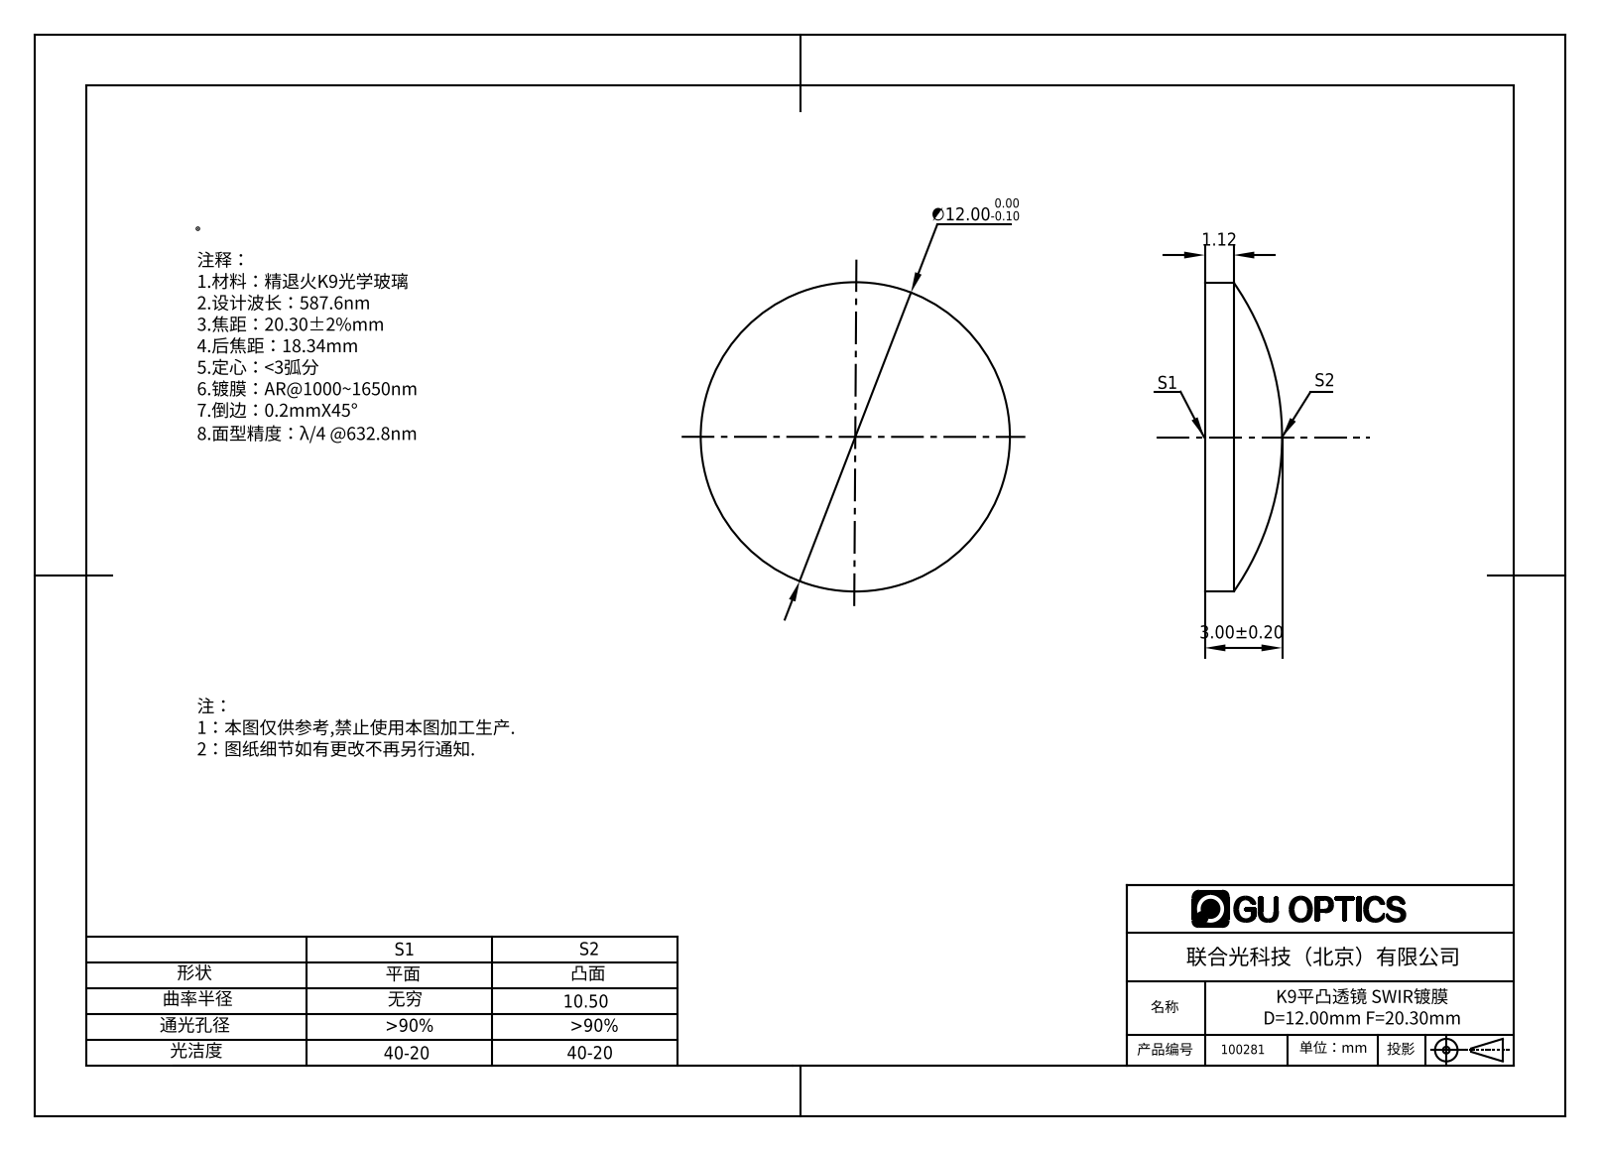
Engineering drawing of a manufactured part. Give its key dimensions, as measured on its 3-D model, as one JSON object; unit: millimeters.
{"part_name": "100109", "step_written_by": "SolidWorks 2016 (AUTOMOTIVE_DESIGN)", "units": "millimeters", "bodies": {"solids": 1, "faces": 5, "planar": 1, "cylindrical": 2, "other": 2}, "overall_size": [12, 12, 3], "volume_mm3": 236, "surface_area_mm2": 280, "round_bosses_or_shafts": [[12, 1]]}
